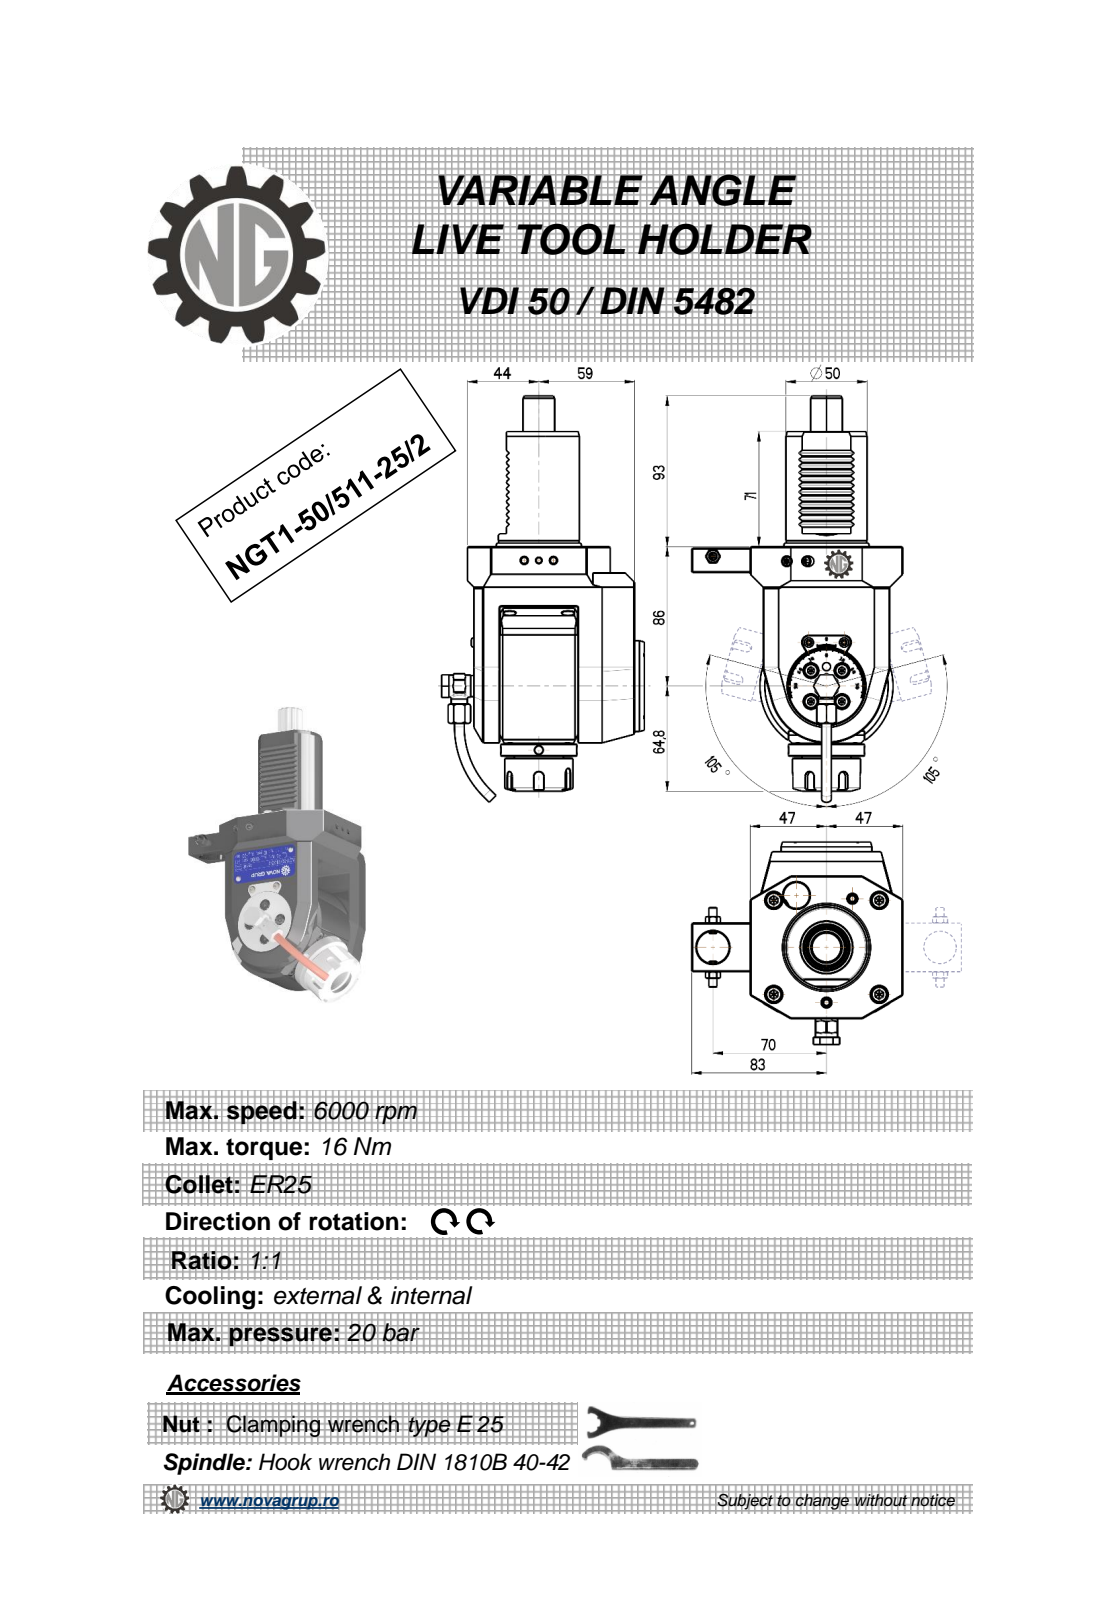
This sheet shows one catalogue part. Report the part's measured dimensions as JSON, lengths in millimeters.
{"part_name": "NGT1_50_511_25_2", "step_written_by": "PRO/ENGINEER BY PARAMETRIC TECHNOLOGY CORPORATION, 2010280 (CONFIG_CONTROL_DESIGN)", "units": "millimeters", "bodies": {"solids": 1, "faces": 667, "planar": 267, "cylindrical": 186, "other": 214}, "overall_size": [250.67, 130, 124.9], "volume_mm3": 1030000, "surface_area_mm2": 91515, "round_holes": [[4, 3], [5, 2], [3, 1], [6.2, 1], [9, 1], [9.5, 1], [10, 1], [11, 1], [20, 1], [20.3, 1]], "round_bosses_or_shafts": [[6, 2], [5.7, 2], [56, 1], [50, 1], [47, 1], [42, 1], [35, 1], [13.6, 1]], "partial_cylinders_radius": [[3.33, 24], [0.26, 12], [0.3, 12], [0.16, 6], [3, 5], [0.5, 4], [1, 2], [10, 2]], "face_to_face_distances": [37, 99, 16, 8, 6, 21, 64, 105, 20, 78], "hole_center_spacings": [0.4, 39.45, 49, 49.4, 70, 85.45, 85.68, 116.95]}
